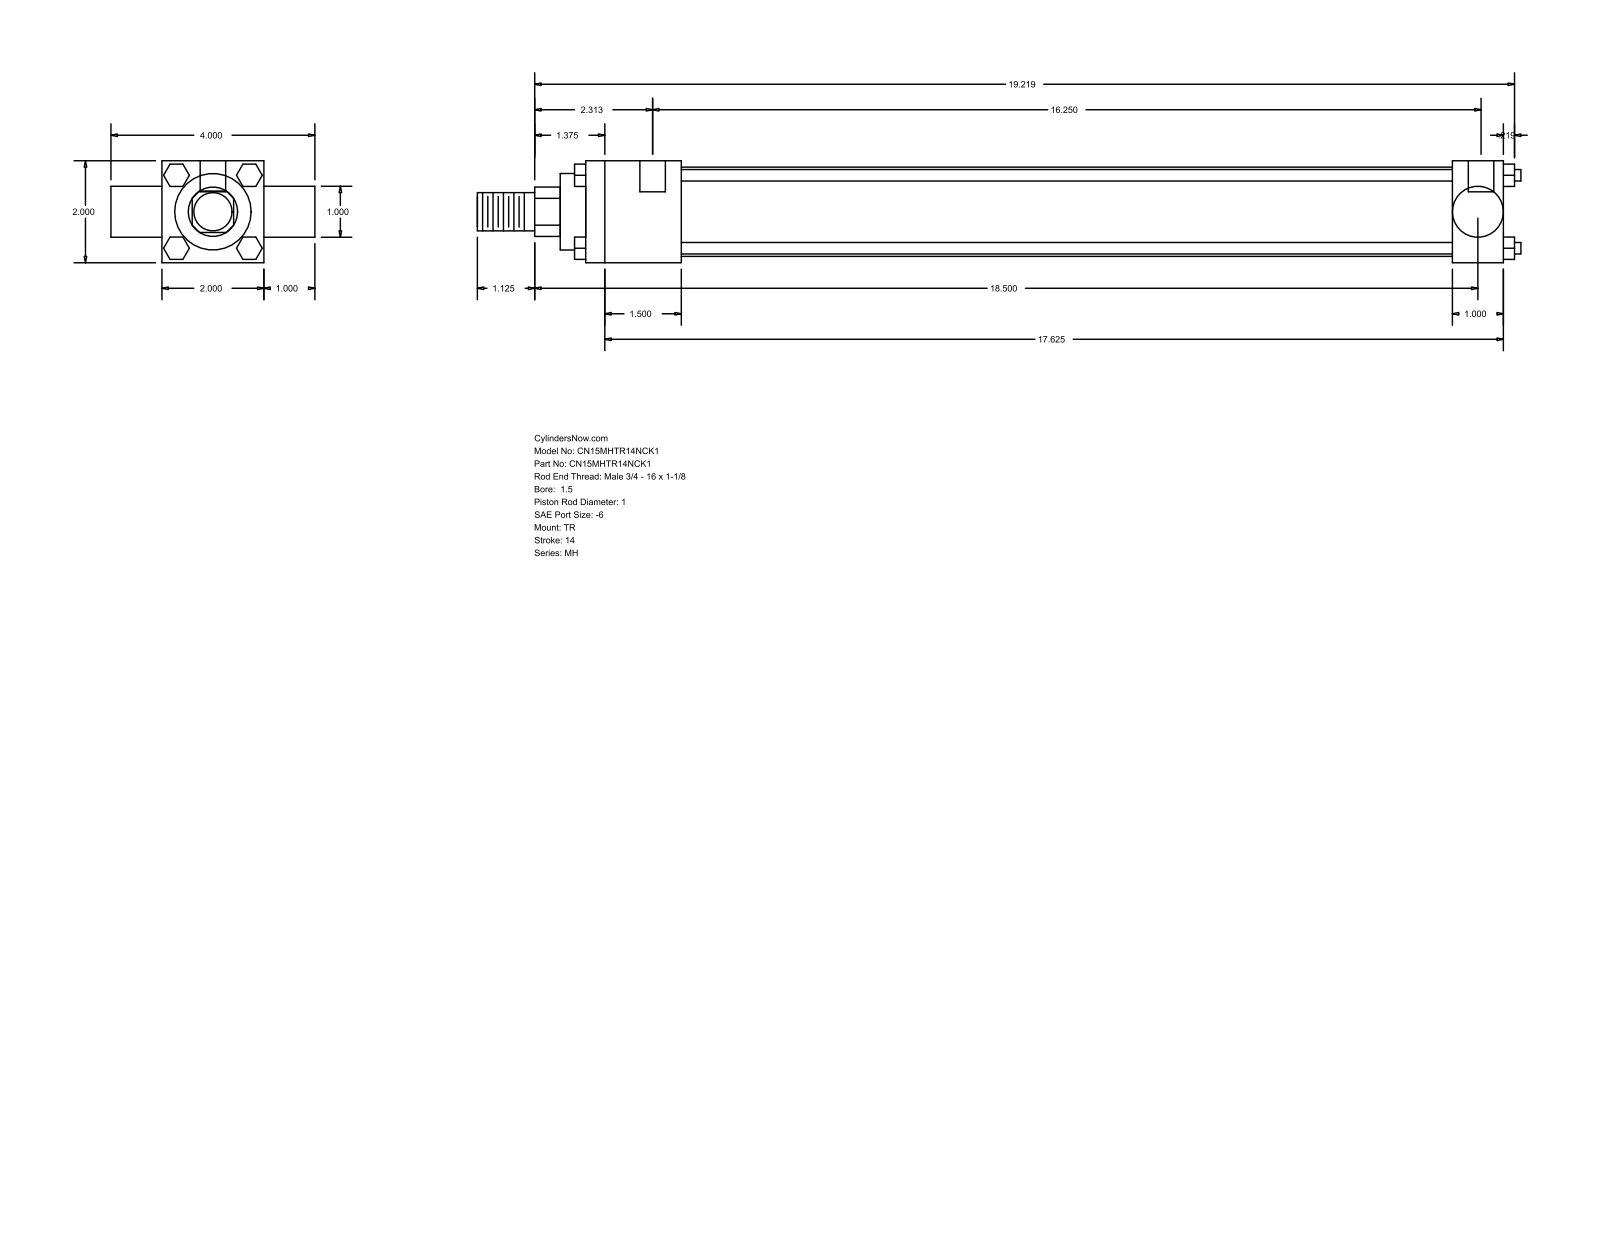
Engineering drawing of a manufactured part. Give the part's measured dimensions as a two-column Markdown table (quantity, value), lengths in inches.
| quantity | value |
| --- | --- |
| part name | MH_TR__0150_1 |
| STEP written by | GSSL Pune (CONFIG_CONTROL_DESIGN) |
| units | inches |
| bodies | 0 solids, 120 faces (92 planar, 28 cylindrical, 0 other) |
| overall size | 20.469 × 4 × 2 |
| round holes (diameter × count) | 0.219 × 3, 0.5 × 2 |
| round bosses / shafts (diameter × count) | 0.225 × 4, 1.75 × 1, 1.5 × 1, 1 × 1, 0.998 × 1, 0.75 × 1 |
| partial cylindrical surfaces (radius × count) | 0.484 × 1 |
| main face-to-face distances | 2, 1, 18, 3, 1.875, 16.125, 17, 15.125, 4, 0.5 |
| hole center spacings | 0.125, 16.25, 16.375 |
